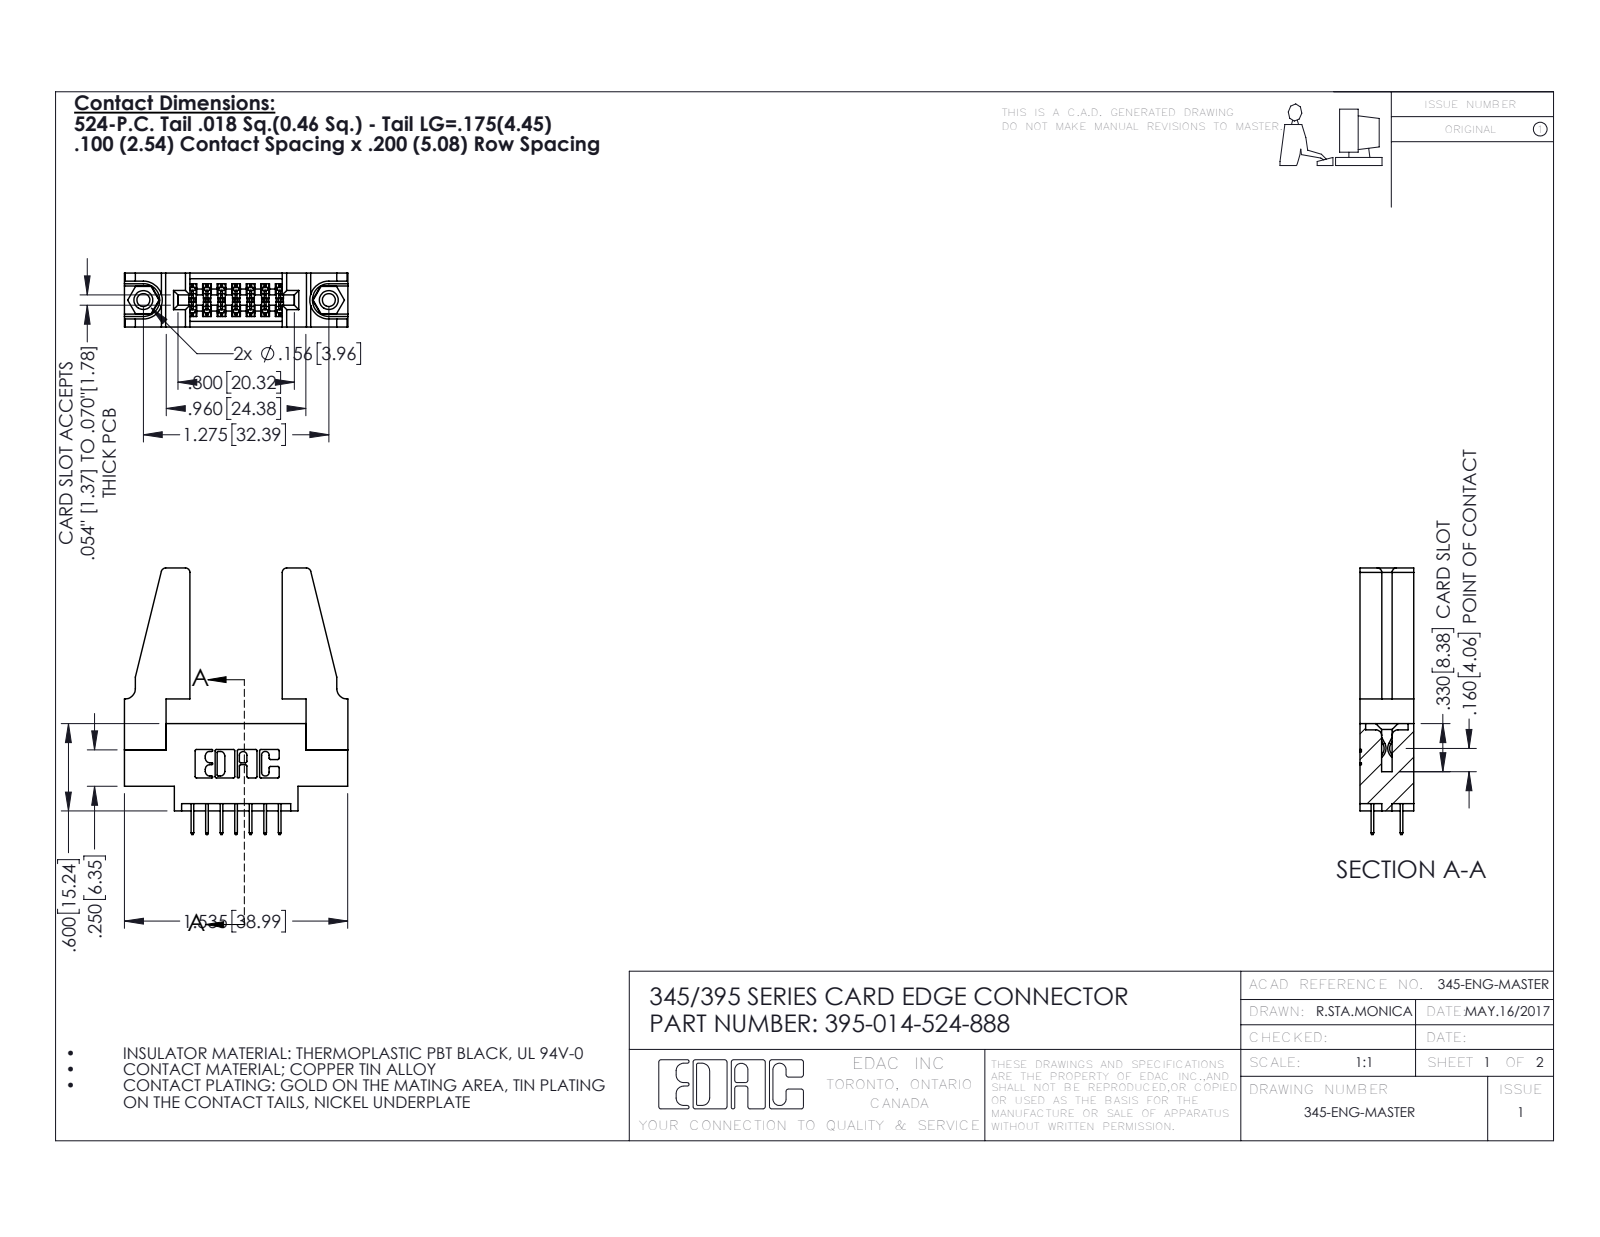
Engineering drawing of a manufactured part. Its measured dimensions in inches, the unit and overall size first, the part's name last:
Units: inches
Overall size (bounding box): 1.832 × 1.536 × 0.37
Round holes (diameter × count): ⌀0.089 ×2, ⌀0.125 ×2, ⌀0.156 ×2, ⌀0.064 ×1
Round bosses / shafts (diameter × count): ⌀0.155 ×2
Partial cylindrical surfaces — rounded edges, fillets, slot ends (radius × count): R0.01 ×22, R0.006 ×21, R0.03 ×8, R0.007 ×6, R0.031 ×6, R0.026 ×3, R0.014 ×2, R0.019 ×2
Main face-to-face distances: 0.37, 0.072, 0.298, 0.2, 0.225, 0.148, 0.15, 0.098, 0.272, 0.025
Hole centre spacings: 0.27, 1.045, 1.275
Volume: 0.402 in³ · Surface area: 11.55 in²
Bodies: 19 solids, 1010 faces (702 planar, 292 cylindrical, 16 other)
Part name (STEP PRODUCT): 345-220-078_345-220-088; 395-014-524-888; 345-250-001_345-250-001-102; 345-292-001_345-293-124 (+1 more)
STEP written by: SolidWorks 2016 (CONFIG_CONTROL_DESIGN)
